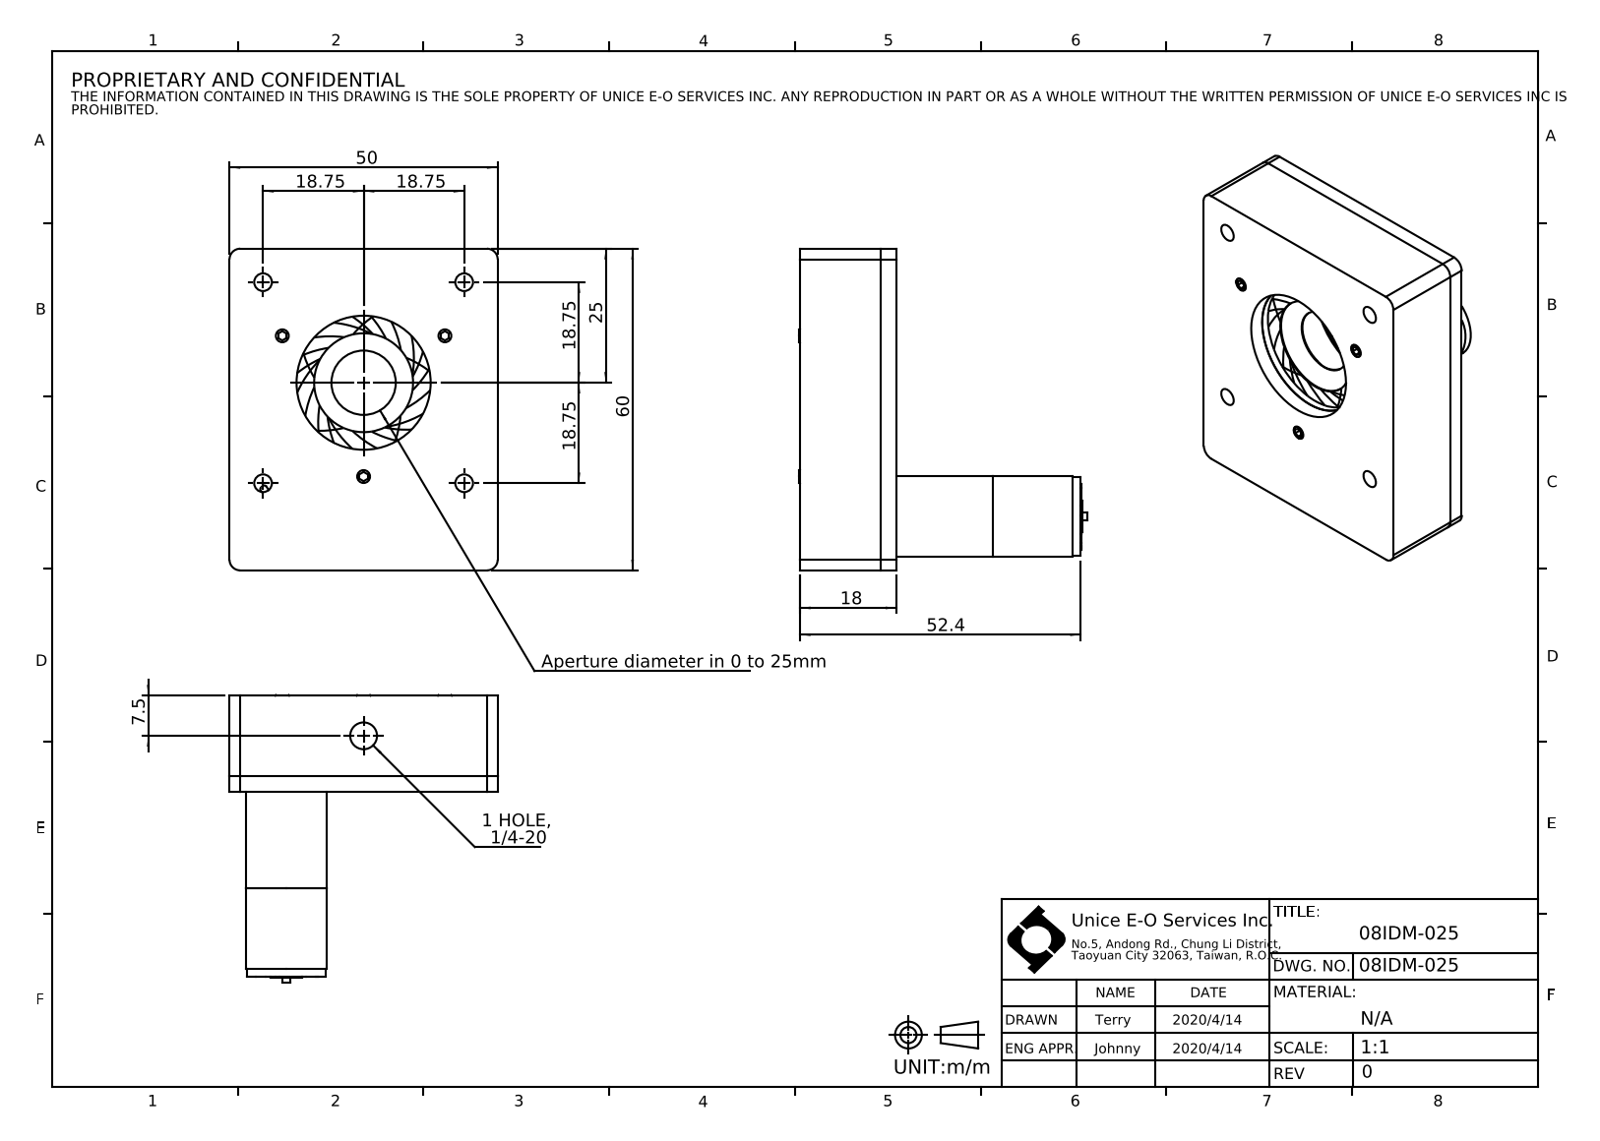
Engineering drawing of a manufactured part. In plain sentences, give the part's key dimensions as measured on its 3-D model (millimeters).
The part is named "08IDM-025". Its 3-D file was written by "SolidWorks 2016 (CONFIG_CONTROL_DESIGN)". It is 0 solids with 214 faces: 124 planar, 74 cylindrical and 16 other. Overall it measures 60 by 53.7 by 50 millimeters. Round holes: 4 of diameter 3.45, 4 of diameter 4.4, 1 of diameter 1.7, 1 of diameter 2.5, 1 of diameter 5.11, 1 of diameter 12, 1 of diameter 18.44, 1 of diameter 25, 1 of diameter 30. Round bosses or shafts: 6 of diameter 1.8, 1 of diameter 15, 1 of diameter 14.8, 1 of diameter 6, 1 of diameter 1.6, 1 of diameter 1.5. Partial cylindrical surfaces (rounded edges, fillets, slot ends): 4 of radius 2. The main face-to-face distances are 18, 9, 50, 60, 15.1, 2.9, 6.1, 6.8, 11.2, 2.2. The hole center spacings are 26.94, 38.1, 41.69, 4.88, 13.89, 31.82, 39.53, 43.67.
